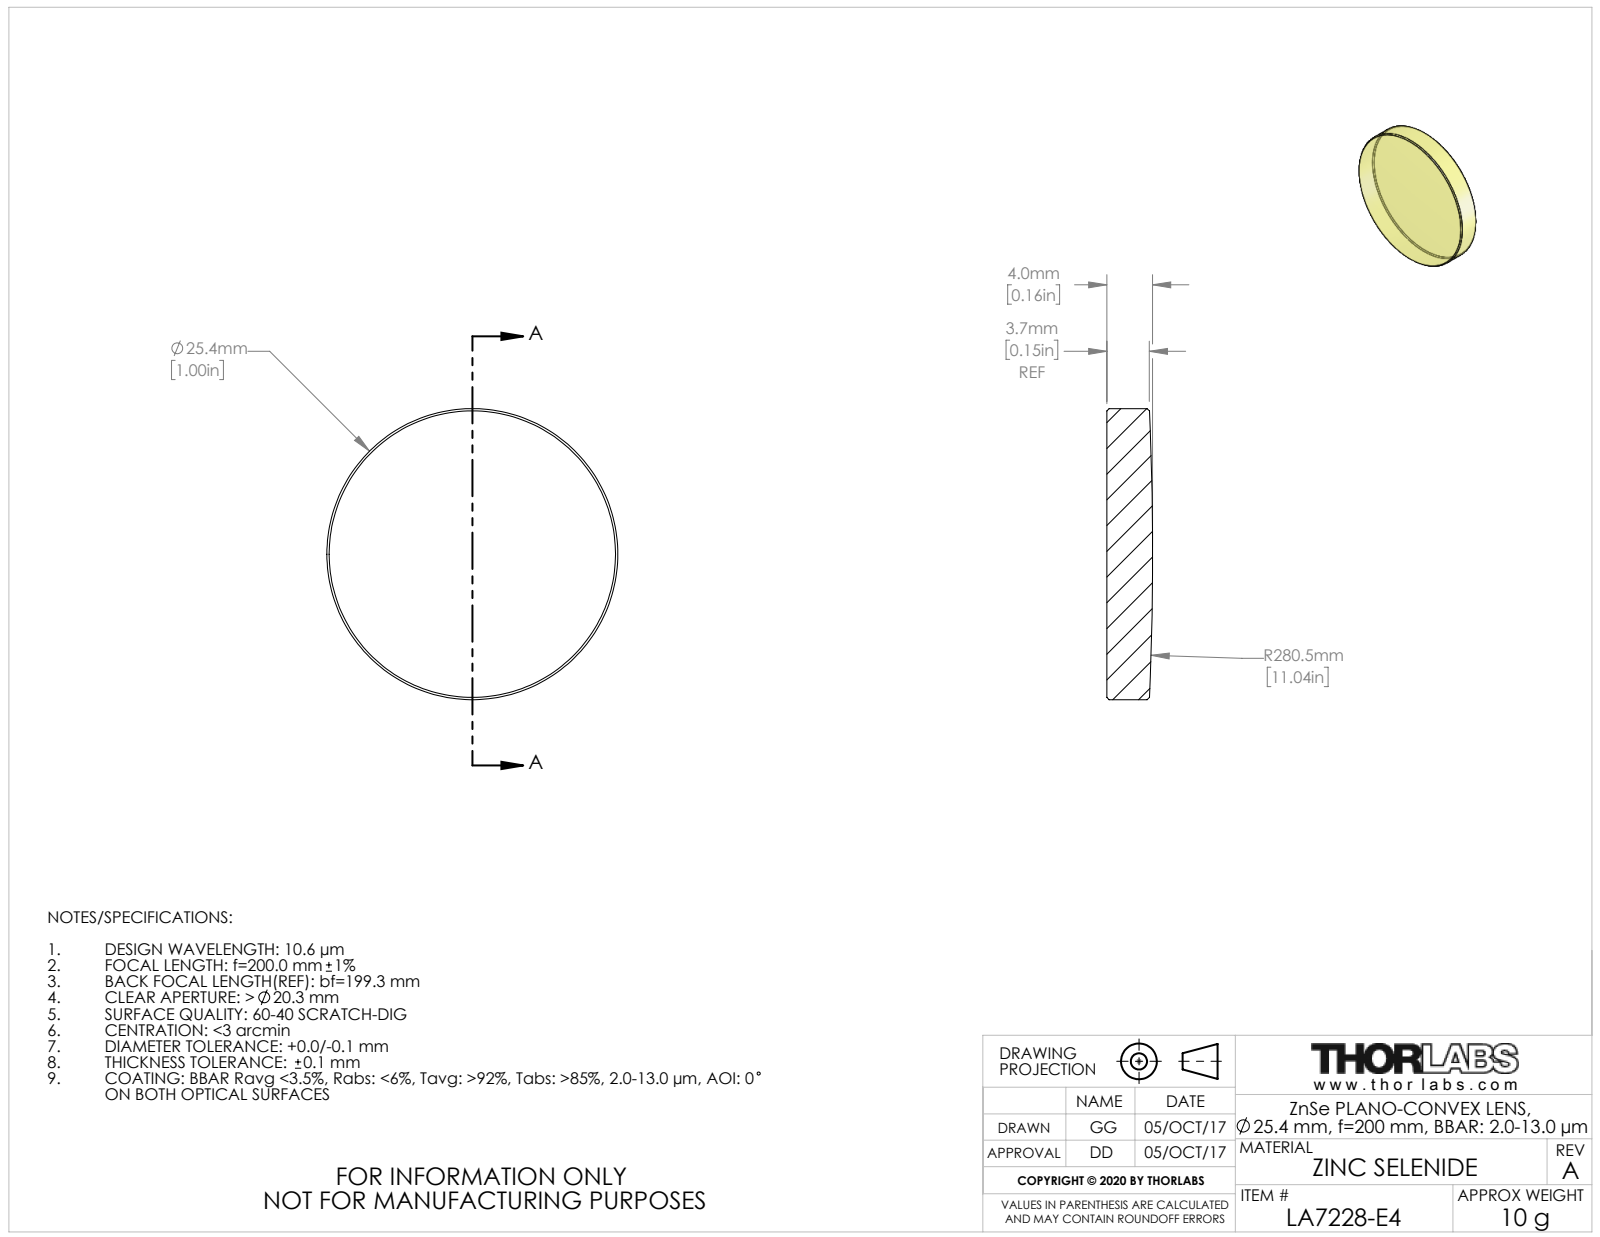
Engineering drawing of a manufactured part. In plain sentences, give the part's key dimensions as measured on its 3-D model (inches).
The part is named "TTN098125-E0W". Its 3-D file was written by "SolidWorks 2018 (CONFIG_CONTROL_DESIGN)". It is 1 solid with 9 faces: 1 planar, 2 cylindrical and 6 other. Overall it measures 1 by 1 by 0.157 inches. Its volume is 0.119 cubic inches and its surface area 2.003 square inches. Round bosses or shafts: 1 of diameter 1.
